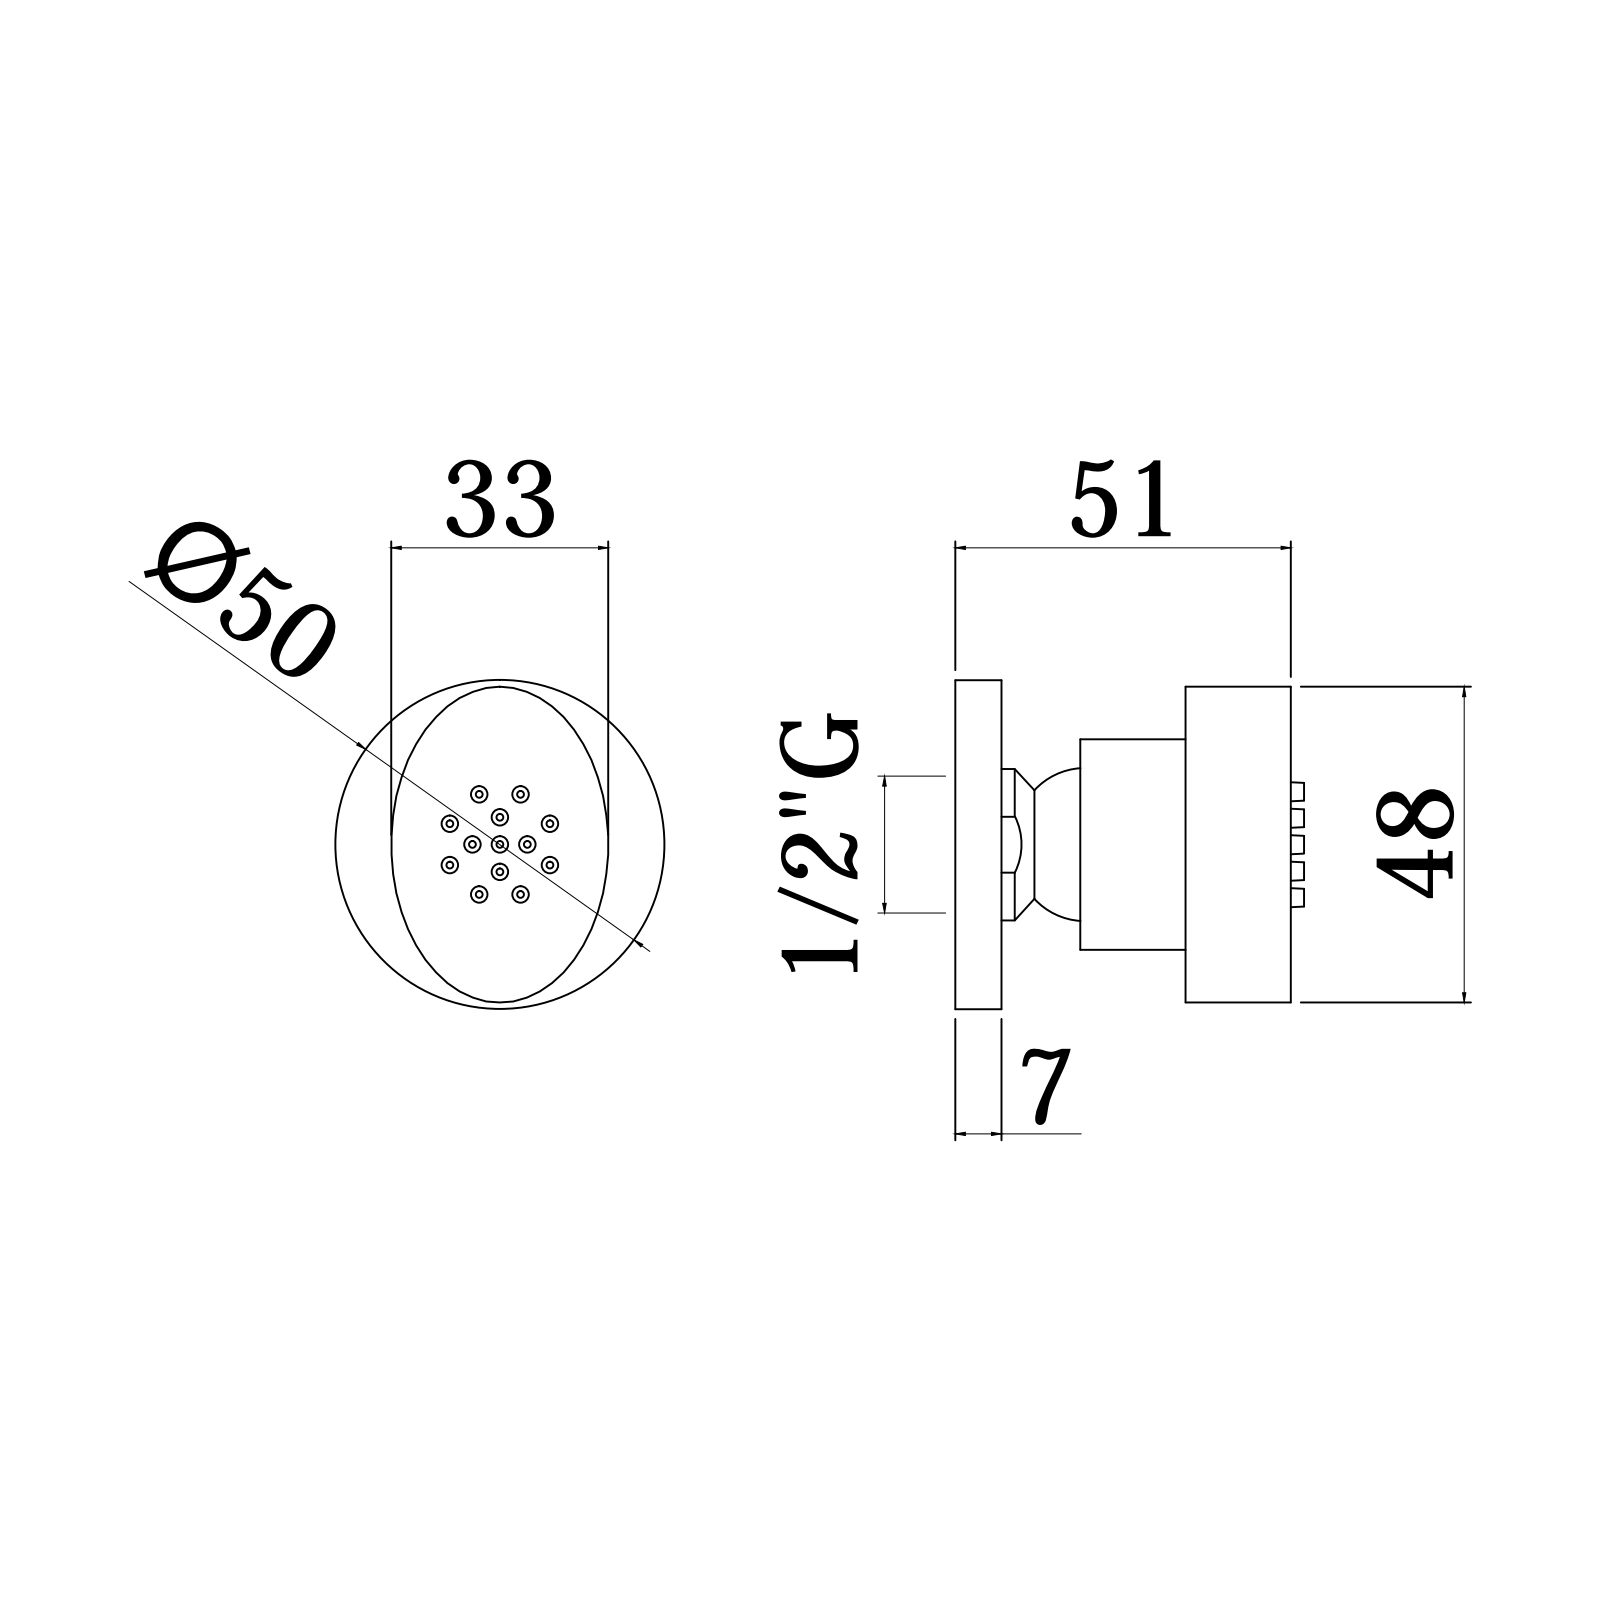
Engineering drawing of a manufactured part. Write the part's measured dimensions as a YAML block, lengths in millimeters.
part_name: "Z242; 22040; Z280; Z103_AF1 (+2 more)"
step_written_by: "CREO PARAMETRIC BY PTC INC, 2020044 (CONFIG_CONTROL_DESIGN)"
units: millimeters
bodies: {solids: 4, faces: 381, planar: 46, cylindrical: 103, other: 232}
overall_size: [53.7, 50, 50]
volume: 24678
surface_area: 21755
round_holes:
  - {diameter: 3, count: 13}
  - {diameter: 7, count: 1}
  - {diameter: 15.15, count: 1}
  - {diameter: 16.5, count: 1}
  - {diameter: 19.75, count: 1}
  - {diameter: 23, count: 1}
  - {diameter: 24, count: 1}
  - {diameter: 24.4, count: 1}
  - {diameter: 25.4, count: 1}
  - {diameter: 26.6, count: 1}
  - {diameter: 28, count: 1}
  - {diameter: 28.1, count: 1}
round_bosses_or_shafts:
  - {diameter: 32, count: 1}
  - {diameter: 27, count: 1}
  - {diameter: 23.2, count: 1}
  - {diameter: 22, count: 1}
  - {diameter: 18, count: 1}
partial_cylinders:
  - {radius: 0.4, count: 2}
face_to_face_distances: [47.2, 2, 16, 31.2, 14, 45.2, 17.2, 4, 12, 43.2]
hole_center_spacings: [4.01, 5.66, 6.94, 7.4, 9.67, 10.47, 11.2, 13.68]
